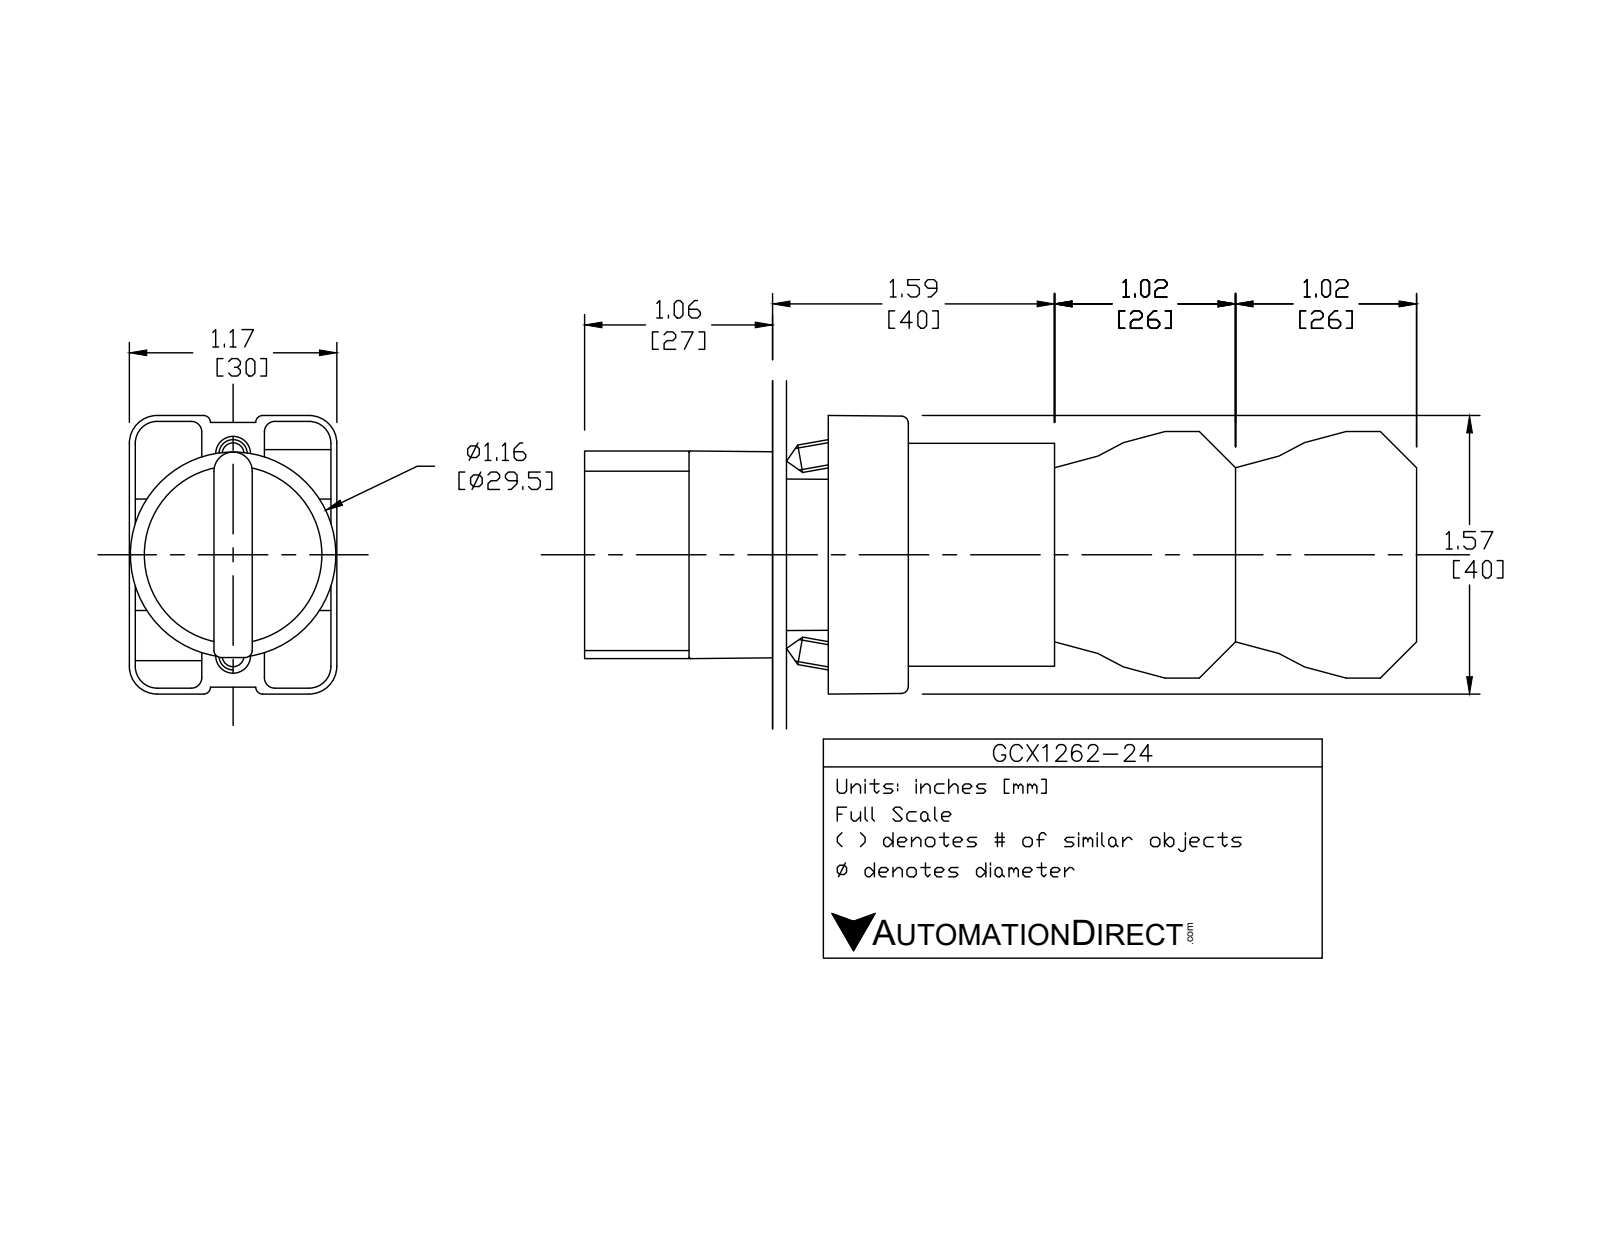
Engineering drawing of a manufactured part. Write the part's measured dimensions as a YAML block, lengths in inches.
part_name: "GCX1262-24"
step_written_by: "SolidWorks 2019 (AUTOMOTIVE_DESIGN)"
units: inches
bodies: {solids: 11, faces: 723, planar: 488, cylindrical: 191, other: 44}
overall_size: [4.677, 1.581, 1.177]
volume: 4.751
surface_area: 59.21
round_holes:
  - {diameter: 0.079, count: 4}
  - {diameter: 0.087, count: 2}
  - {diameter: 0.124, count: 2}
  - {diameter: 0.13, count: 2}
  - {diameter: 0.469, count: 1}
  - {diameter: 0.878, count: 1}
  - {diameter: 0.888, count: 1}
  - {diameter: 1.024, count: 1}
round_bosses_or_shafts:
  - {diameter: 0.157, count: 4}
  - {diameter: 1.175, count: 1}
  - {diameter: 1.004, count: 1}
  - {diameter: 0.945, count: 1}
  - {diameter: 0.856, count: 1}
  - {diameter: 0.78, count: 1}
  - {diameter: 0.504, count: 1}
partial_cylinders:
  - {radius: 0.059, count: 24}
  - {radius: 0.041, count: 12}
  - {radius: 0.124, count: 12}
  - {radius: 0.157, count: 12}
  - {radius: 0.039, count: 9}
  - {radius: 0.02, count: 2}
  - {radius: 0.063, count: 2}
  - {radius: 0.079, count: 2}
face_to_face_distances: [0.598, 0.579, 1.024, 1.177, 0.02, 0.827, 1.85, 1.171, 0.573, 0.593]
hole_center_spacings: [0.236, 0.544, 1.008, 0.98, 0.472, 0.49, 1.088]
